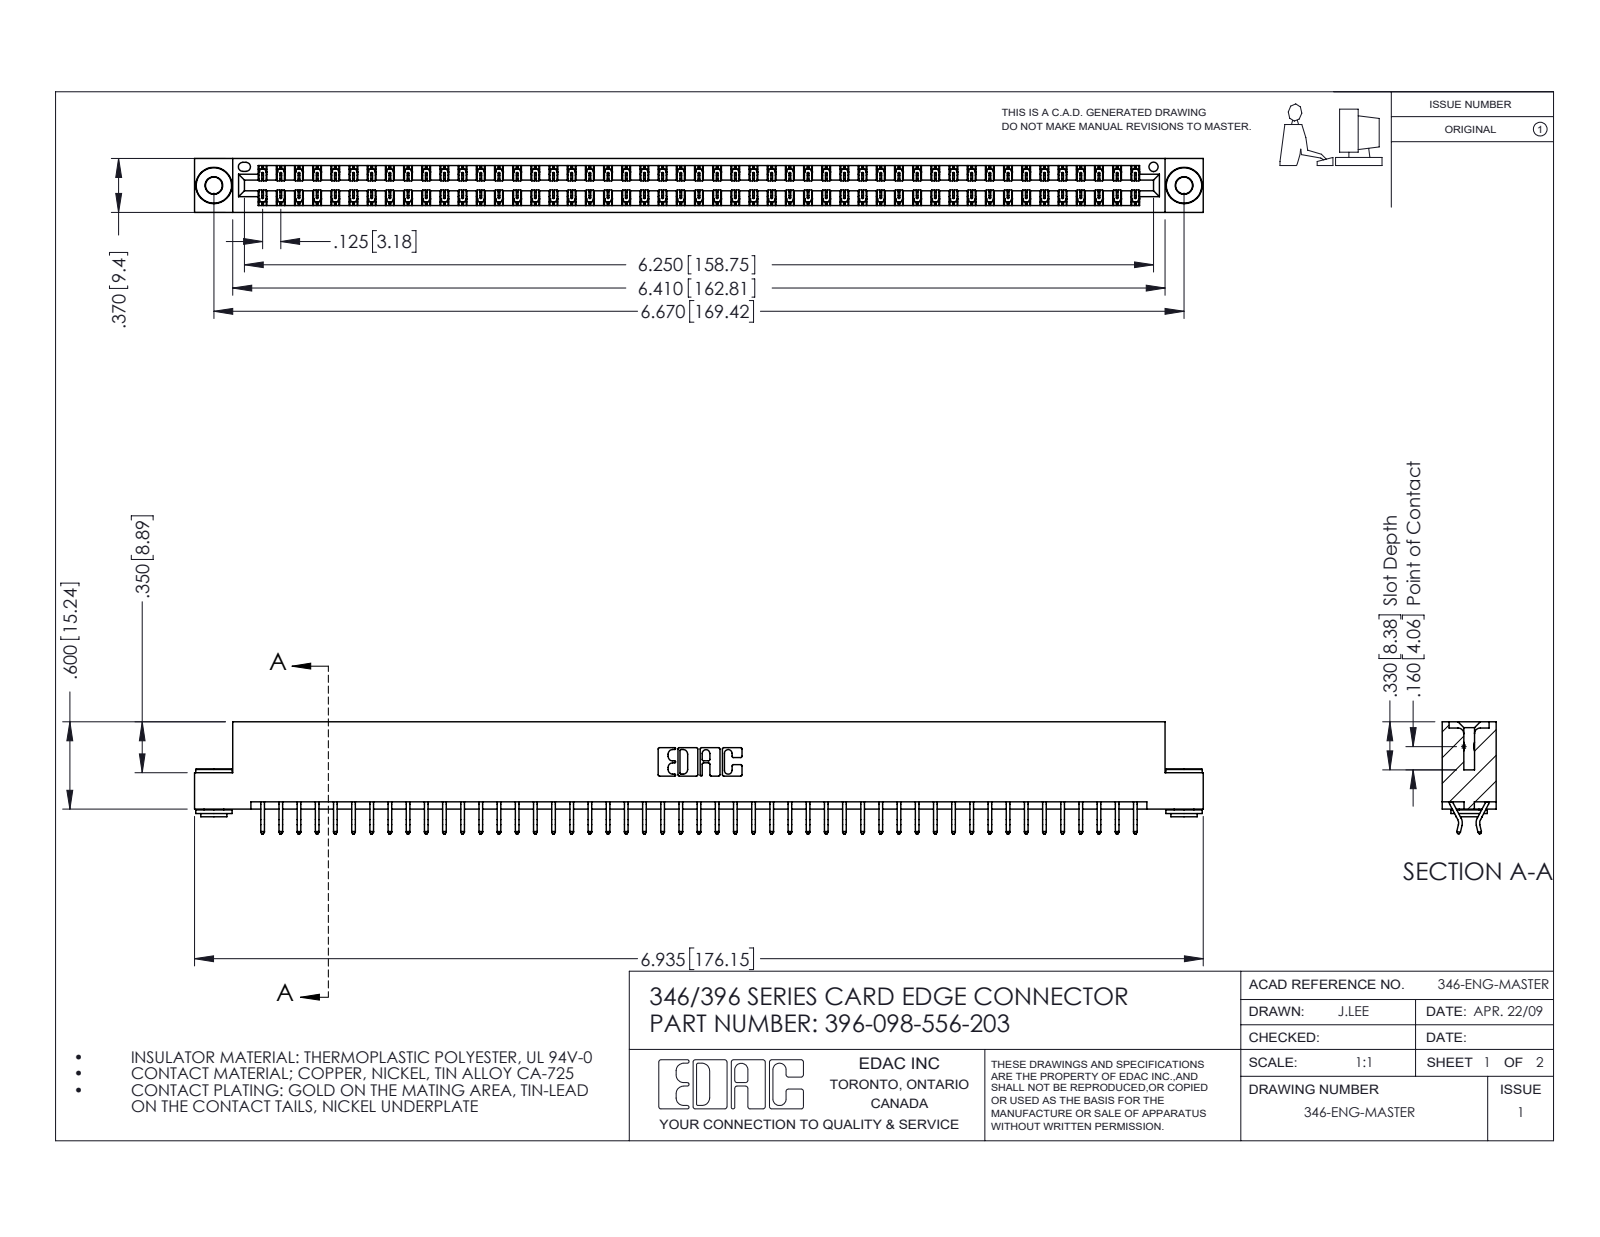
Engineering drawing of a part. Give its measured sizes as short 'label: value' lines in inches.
name: 396-098-556-203; 345-250-002_345-250-002-102; 345-292-001_556 Tail; 346 Part_Flush Mounting Lugs - 0.156 Dia-TH
written by: SolidWorks 2016 (CONFIG_CONTROL_DESIGN)
unit: in
bodies: 101 solids, 5844 faces (3908 planar, 1928 cylindrical, 8 other)
size: 6.935 × 0.77 × 0.37
volume: 1.052 in³; area: 37.11 in²
holes: 2× ⌀0.116, 2× ⌀0.156, 1× ⌀0.064
bosses: 2× ⌀0.25, 2× ⌀0.18, 2× ⌀0.136
rounds: 147× R0.006, 22× R0.01, 6× R0.007, 6× R0.031, 3× R0.026, 2× R0.01, 2× R0.014, 2× R0.022
face distances: 0.048, 0.322, 0.37, 0.25, 0.025, 0.072, 0.298, 0.275, 0.148, 0.222
hole spacings: 0.246, 6.461, 6.67
